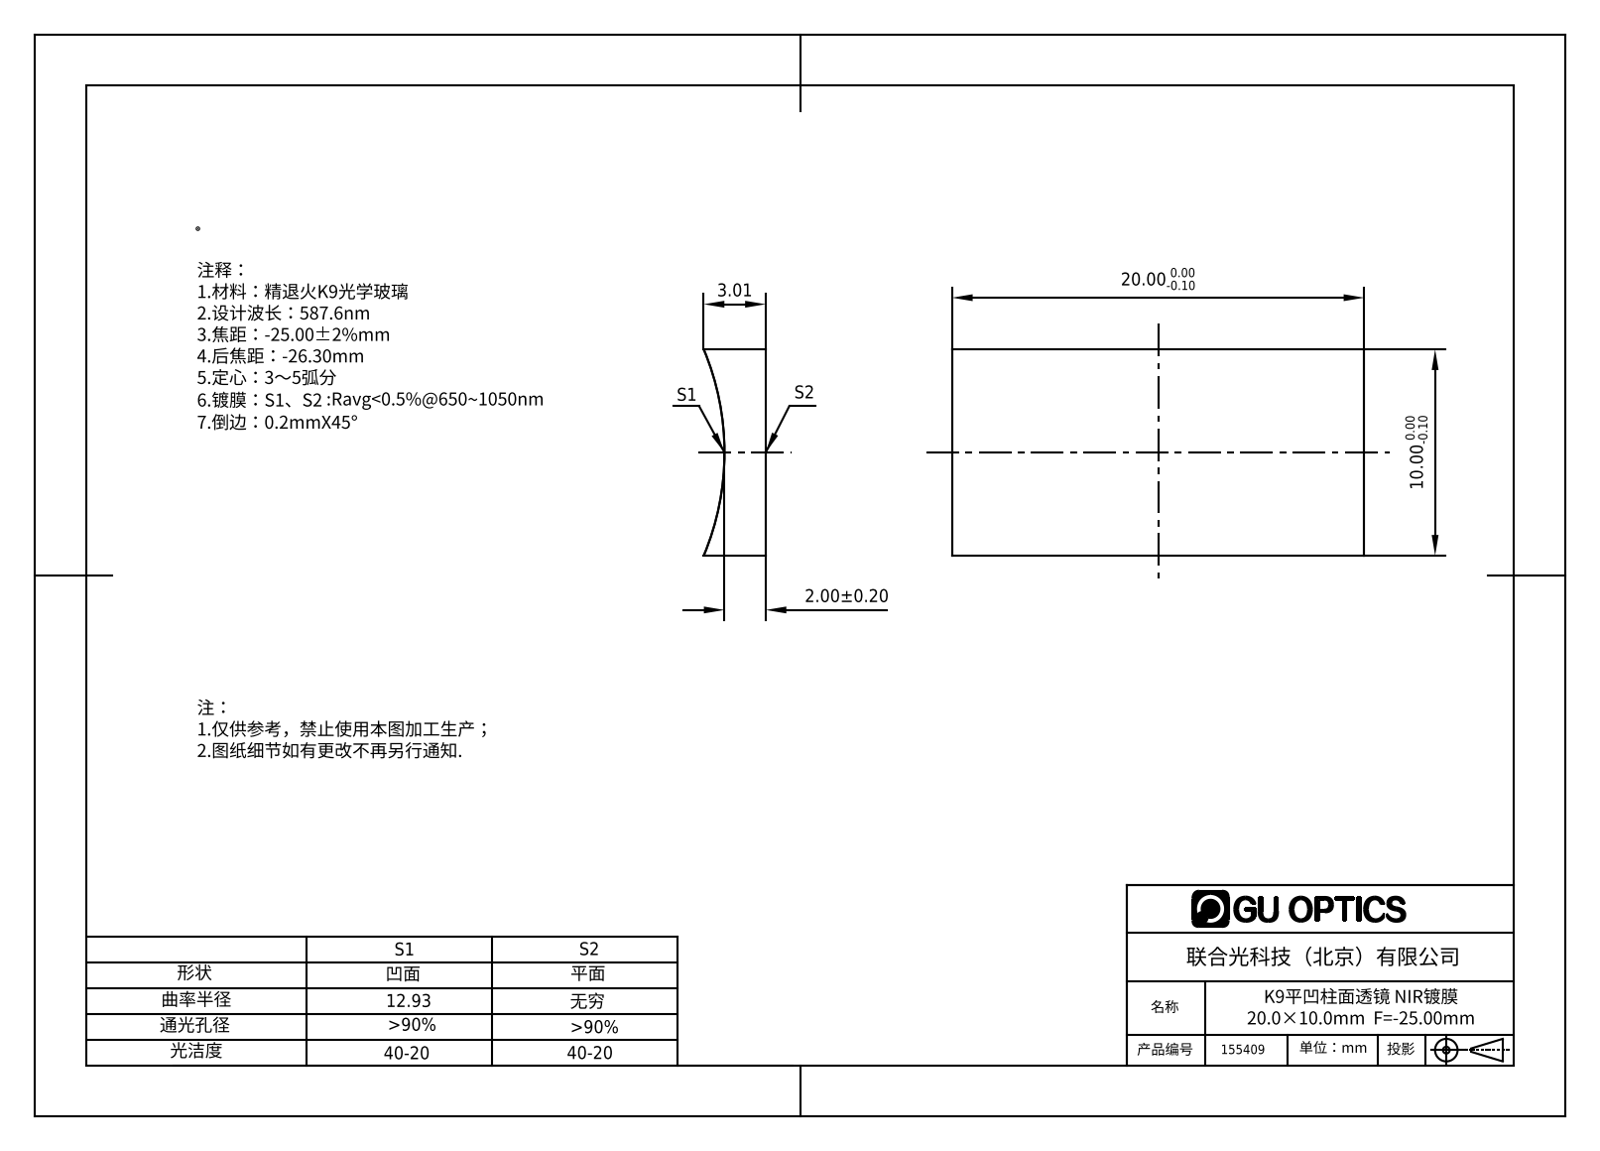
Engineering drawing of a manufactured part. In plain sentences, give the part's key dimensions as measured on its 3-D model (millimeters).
The part is named "155343". Its 3-D file was written by "SolidWorks 2016 (AUTOMOTIVE_DESIGN)". It is 1 solid with 6 faces: 5 planar, 1 cylindrical and 0 other. Overall it measures 20 by 10 by 3.01 millimeters. Its volume is 466 cubic millimeters and its surface area 572 square millimeters. Partial cylindrical surfaces (rounded edges, fillets, slot ends): 1 of radius 12.93. The main face-to-face distances are 10, 20.
